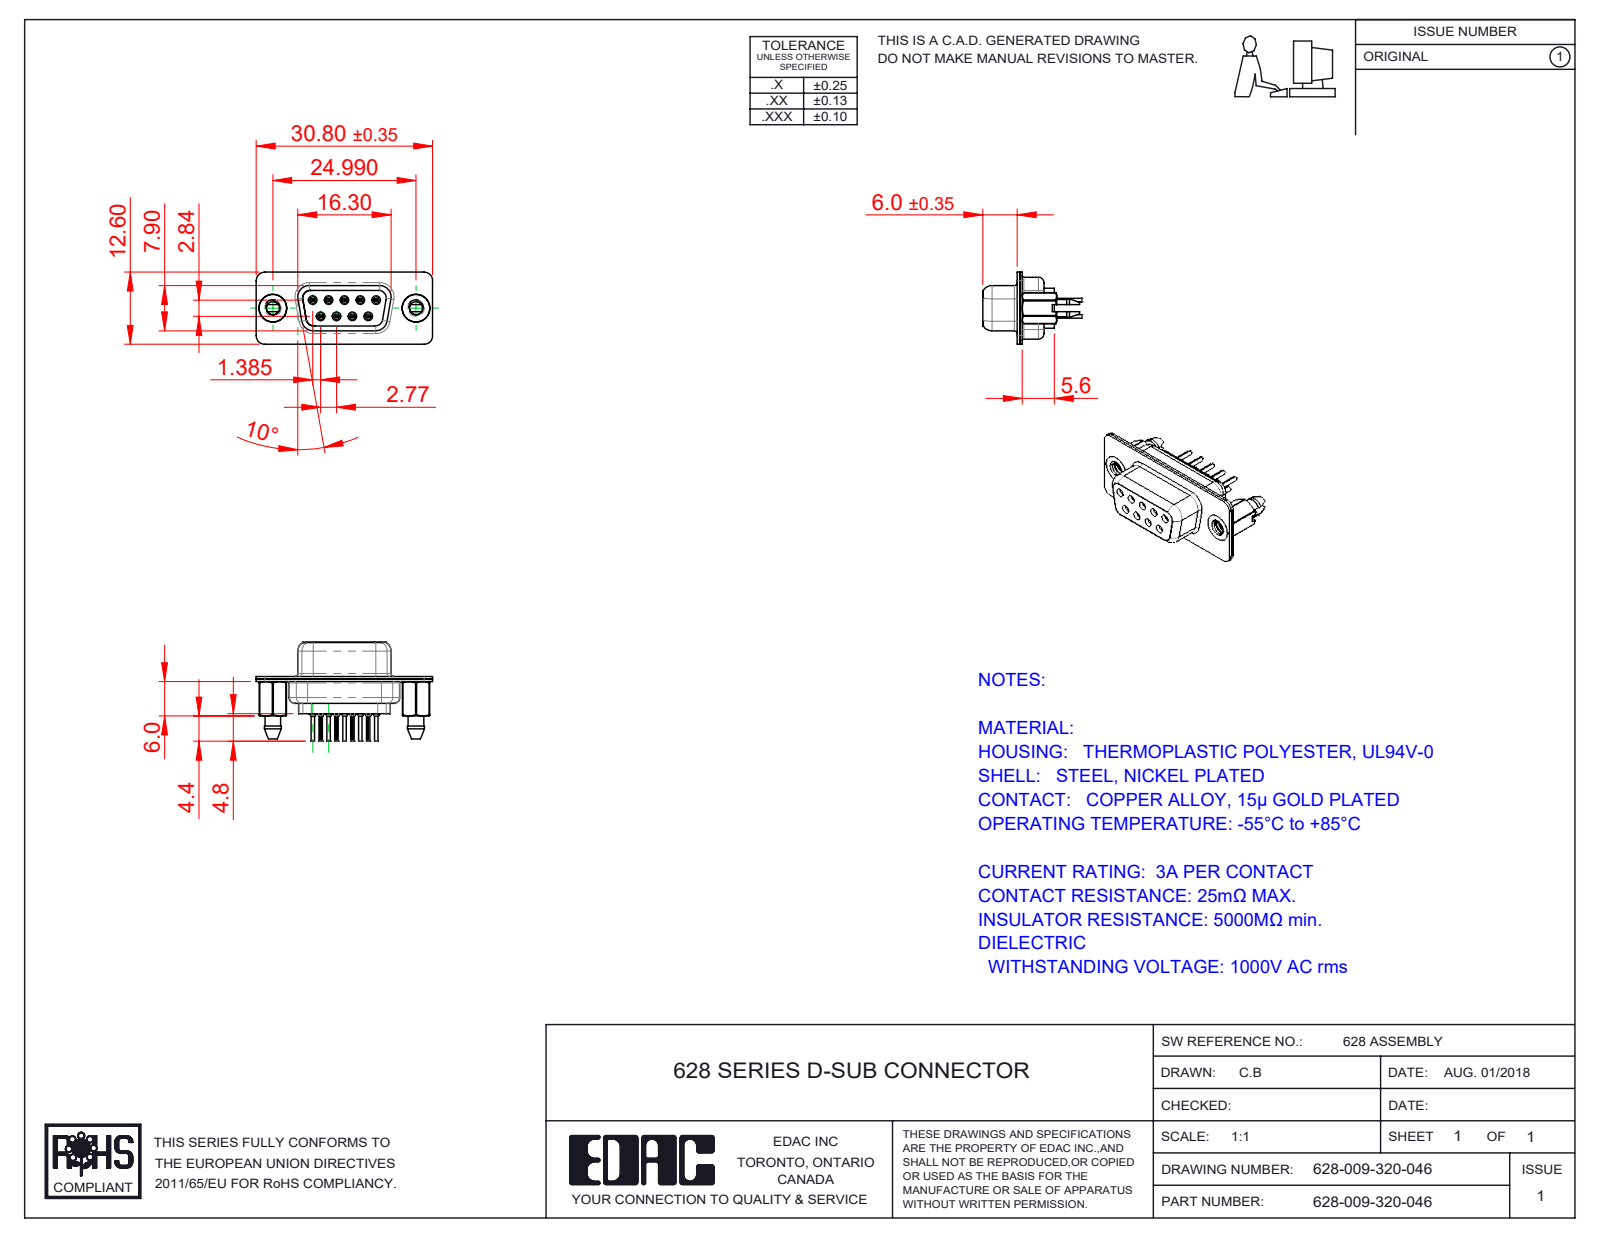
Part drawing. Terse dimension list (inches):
name: 628 Housing_09 LP; 628 Contact Row 2_20L; 628 4-40 Threaded Boardlock_LP; 628 Shell Rear_09 Contacts (+3 more)
written by: SolidWorks 2020 (CONFIG_CONTROL_DESIGN)
unit: in
bodies: 14 solids, 1496 faces (378 planar, 466 cylindrical, 652 other)
size: 1.213 × 0.681 × 0.496
volume: 0.114 in³; area: 7.438 in²
holes: 9× ⌀0.008, 9× ⌀0.031, 9× ⌀0.035, 9× ⌀0.043, 9× ⌀0.063, 5× ⌀0.067, 2× ⌀0.089, 2× ⌀0.157, 2× ⌀0.159, 2× ⌀0.191
bosses: 9× ⌀0.079, 9× ⌀0.059, 9× ⌀0.047, 9× ⌀0.024, 2× ⌀0.195, 2× ⌀0.189
rounds: 19× R0.059, 18× R0.004, 12× R0.079, 9× R0.011, 6× R0.053, 6× R0.063, 4× R0.01, 4× R0.02
face distances: 0.018, 0.016, 0.035, 0.075, 0.335, 0.26, 0.055, 0.02, 0.256, 0.492
hole spacings: 0.124, 0.109, 0.218, 0.198, 0.198, 0.327, 0.294, 0.295
